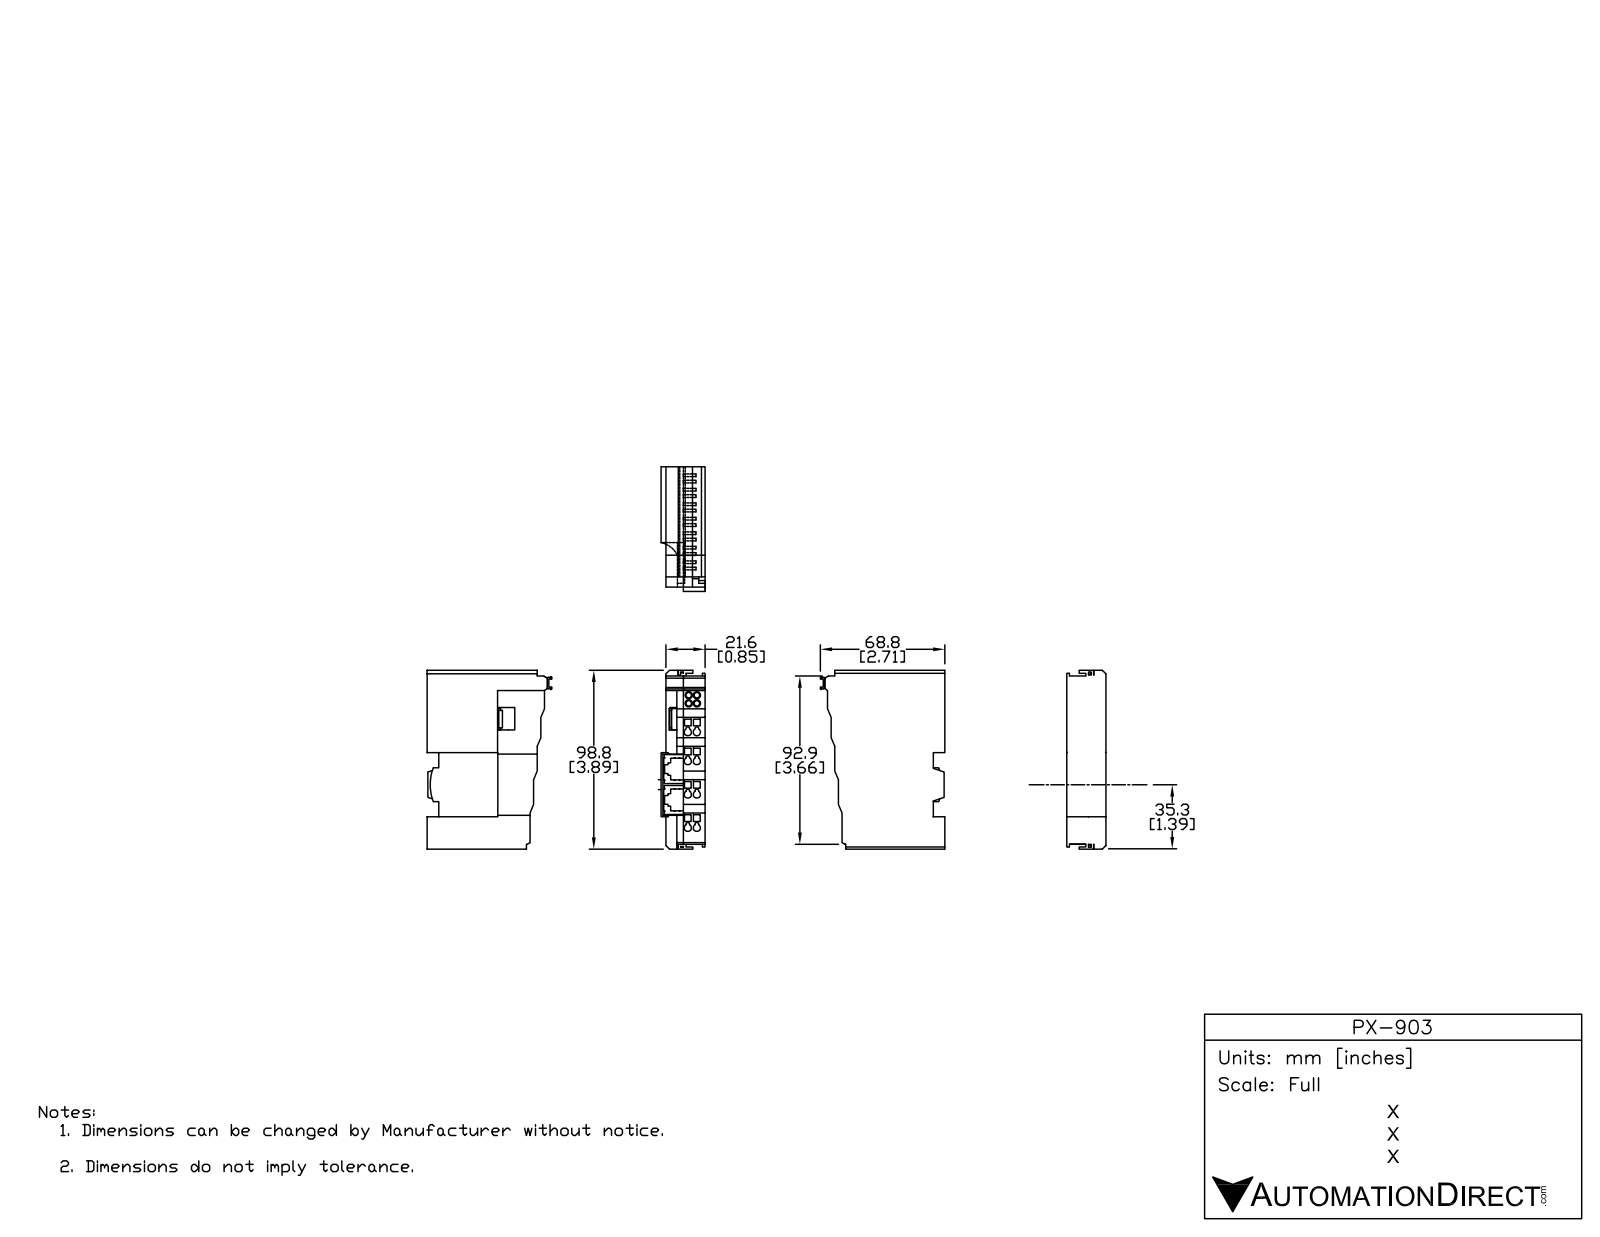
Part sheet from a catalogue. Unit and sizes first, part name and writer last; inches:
Units: inches
Overall size (bounding box): 3.947 × 2.806 × 1.01
Round holes (diameter × count): ⌀0.157 ×8, ⌀0.138 ×4
Partial cylindrical surfaces — rounded edges, fillets, slot ends (radius × count): R0.012 ×46, R0.01 ×35, R0.015 ×12, R0.005 ×10, R0.039 ×9, R0.016 ×8, R0.007 ×4, R0.041 ×4
Main face-to-face distances: 0.394, 0.866, 0.472, 0.039, 0.512, 0.433, 0.118, 0.984, 0.014, 0.073
Hole centre spacings: 0.177, 0.197, 0.724, 0.751, 0.25, 0.63, 0.66, 0.804
Volume: 6.323 in³ · Surface area: 74.79 in²
Bodies: 39 solids, 1760 faces (1252 planar, 352 cylindrical, 156 other)
Part name (STEP PRODUCT): PX-903
STEP written by: SolidWorks 2014 (AUTOMOTIVE_DESIGN)
